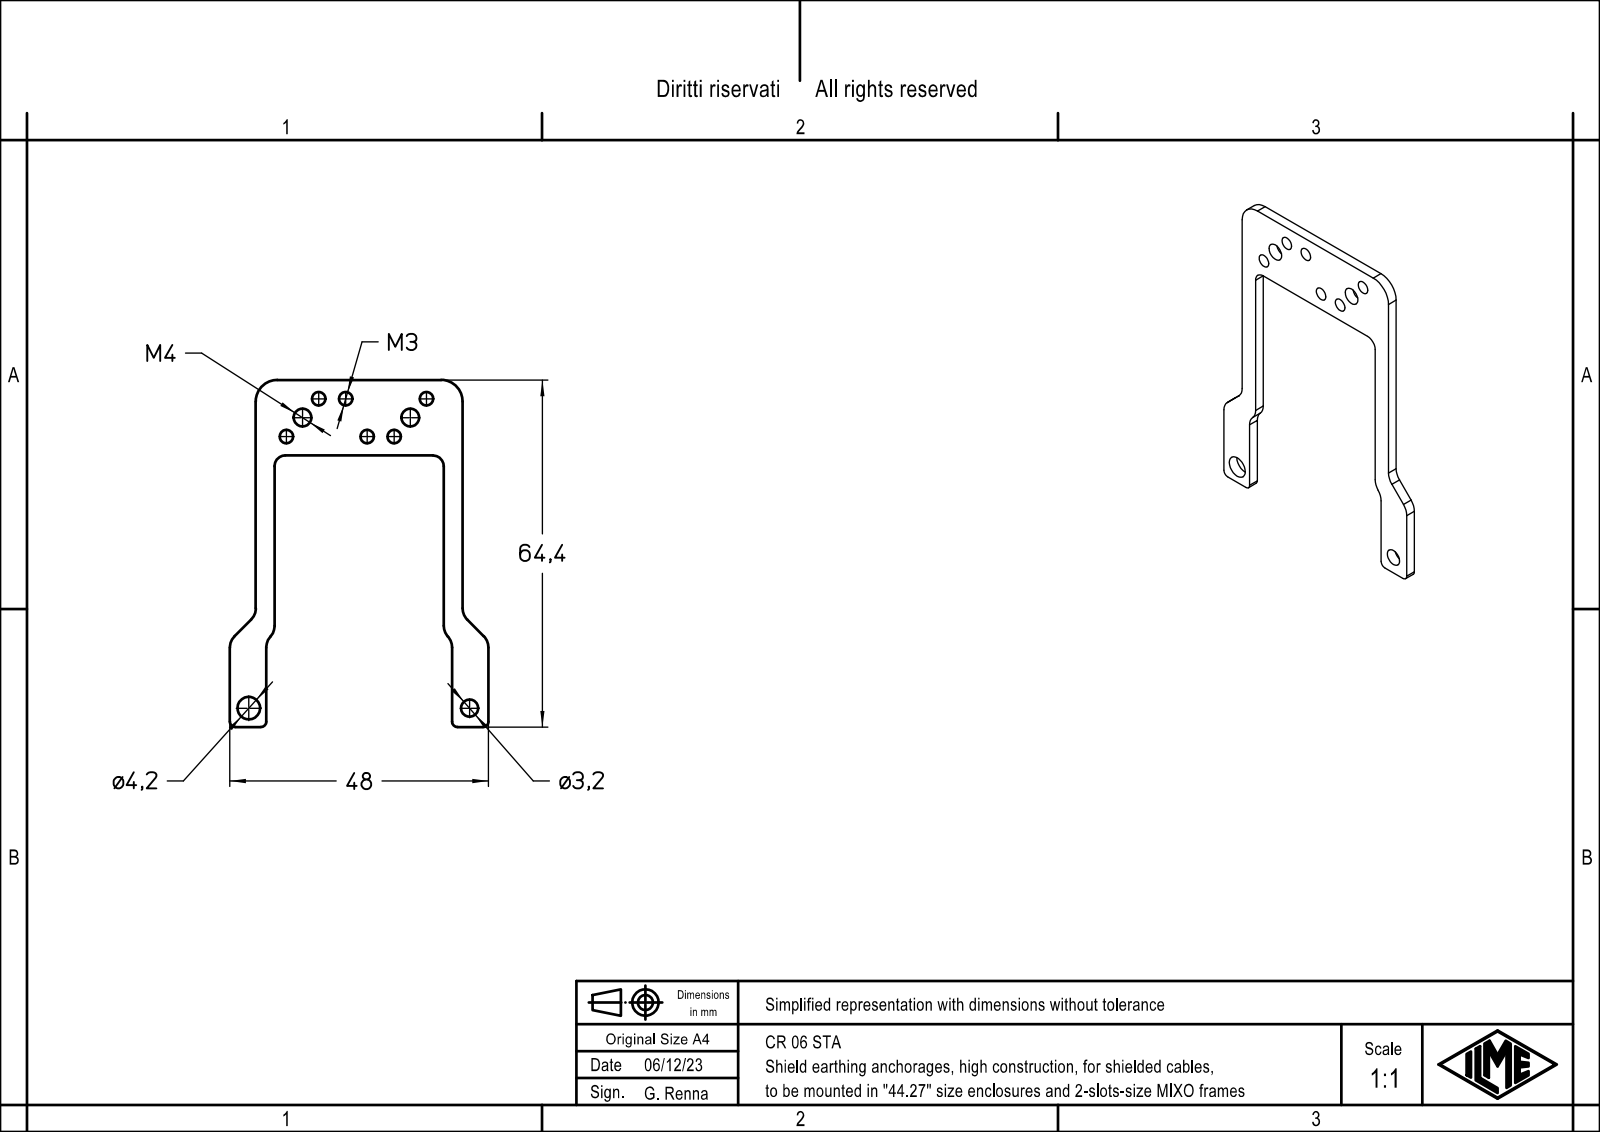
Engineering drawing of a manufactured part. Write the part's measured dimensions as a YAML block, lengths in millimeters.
part_name: "CR_06_STA"
step_written_by: "Creo Elements/Direct Modeling 20.5B 27-May-2023 (C) Parametric Technology GmbH (AUTOMOTIVE_DESIGN)"
units: millimeters
bodies: {solids: 1, faces: 52, planar: 16, cylindrical: 36, other: 0}
overall_size: [64.4, 48, 2]
volume: 1881
surface_area: 2684
round_holes:
  - {diameter: 2.5, count: 6}
  - {diameter: 3.3, count: 2}
  - {diameter: 3.2, count: 1}
  - {diameter: 4.2, count: 1}
partial_cylinders:
  - {radius: 3, count: 8}
  - {radius: 1, count: 4}
  - {radius: 2, count: 2}
  - {radius: 4, count: 2}
face_to_face_distances: [2, 3.5, 34.9, 38.4, 31.4, 1.95, 36.45, 1.55, 32.95, 4.8]
hole_center_spacings: [4.61, 20, 5, 8.73, 9.22, 11.4, 12.5, 13.04]
